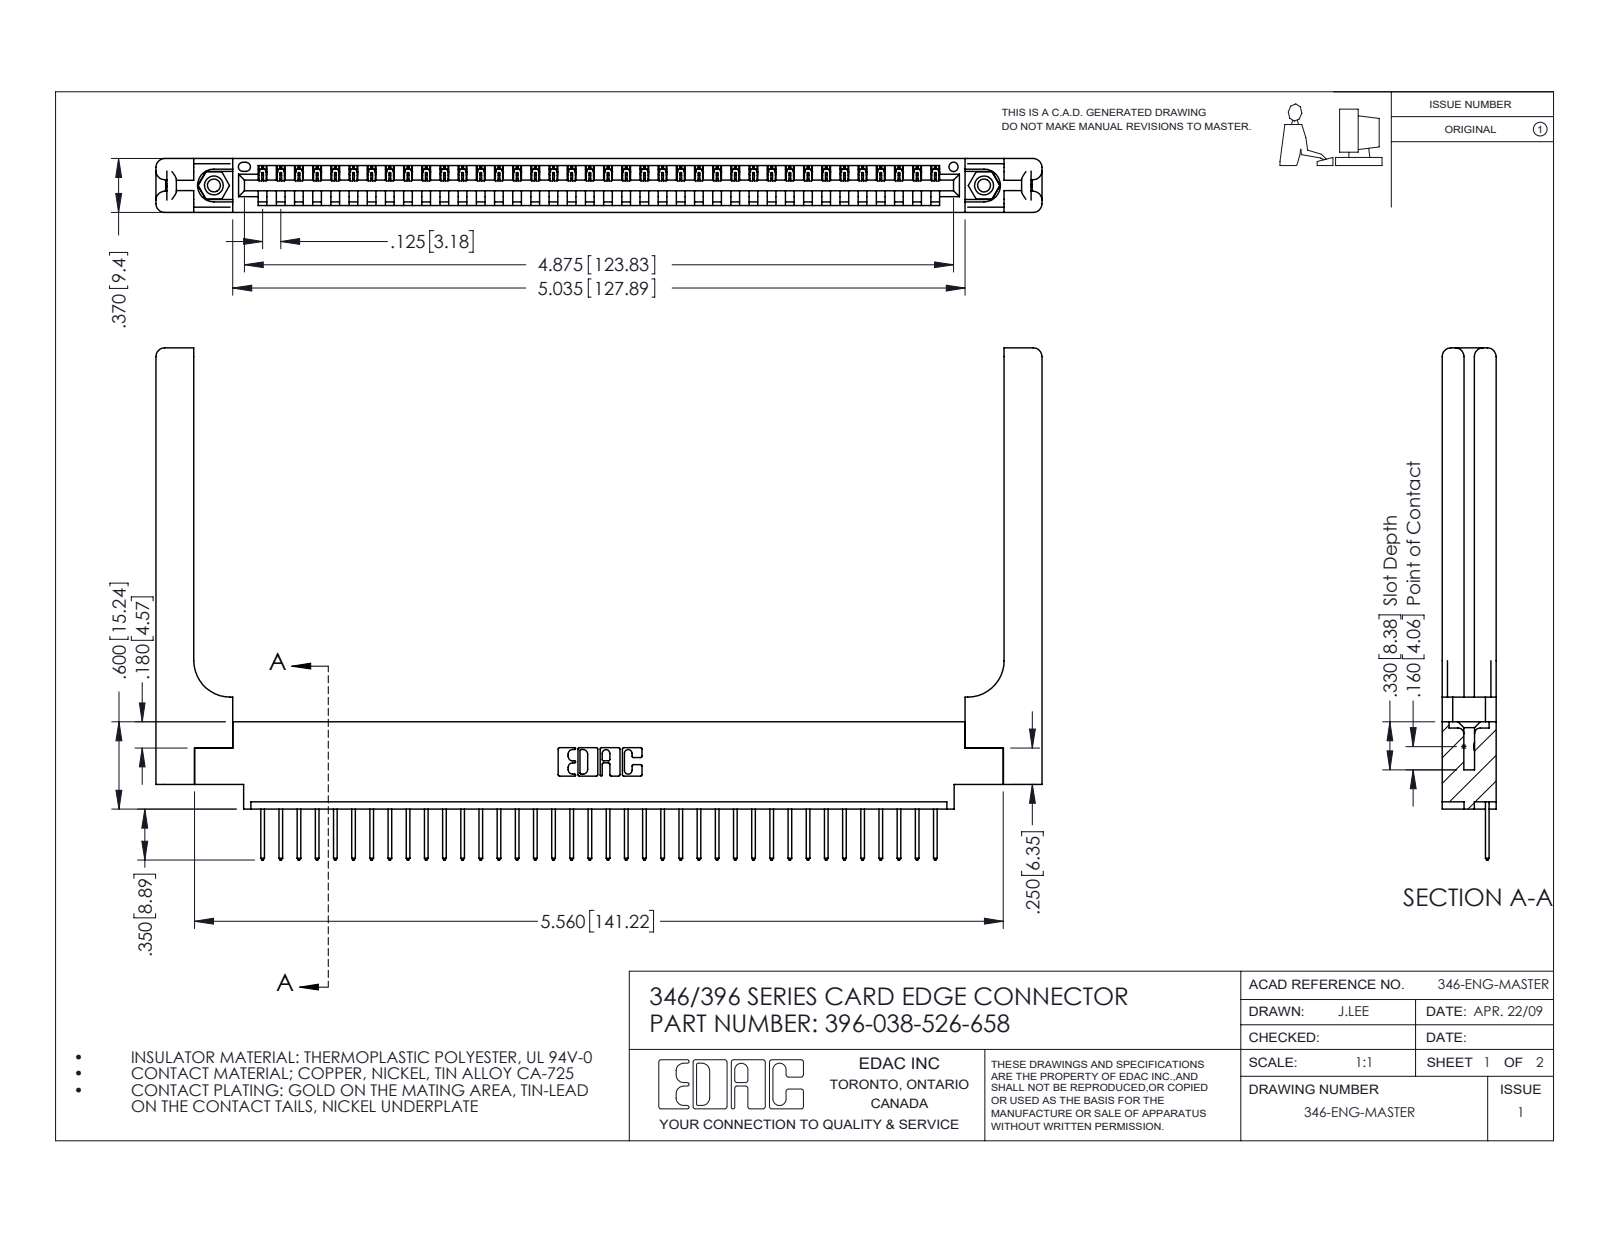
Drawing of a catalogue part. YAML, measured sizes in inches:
part_name: "345-292-001_345-293-126; 396-038-526-658; 346-220-058_345-220-058; 346 Part_0.170 Offset - 0.156 Dia-TH (+1 more)"
step_written_by: "SolidWorks 2016 (CONFIG_CONTROL_DESIGN)"
units: inches
bodies: {solids: 43, faces: 2586, planar: 1748, cylindrical: 778, other: 60}
overall_size: [6.091, 3.52, 0.37]
volume: 1.35
surface_area: 36.42
round_holes:
  - {diameter: 0.089, count: 2}
  - {diameter: 0.125, count: 2}
  - {diameter: 0.156, count: 2}
  - {diameter: 0.064, count: 1}
round_bosses_or_shafts:
  - {diameter: 0.155, count: 2}
partial_cylinders:
  - {radius: 0.006, count: 76}
  - {radius: 0.01, count: 76}
  - {radius: 0.01, count: 22}
  - {radius: 0.06, count: 16}
  - {radius: 0.007, count: 6}
  - {radius: 0.031, count: 6}
  - {radius: 0.026, count: 3}
  - {radius: 0.03, count: 2}
face_to_face_distances: [0.37, 0.048, 0.322, 0.072, 0.148, 0.15, 0.25, 0.298, 0.025, 0.222]
hole_center_spacings: [0.246, 5.086, 5.295]
